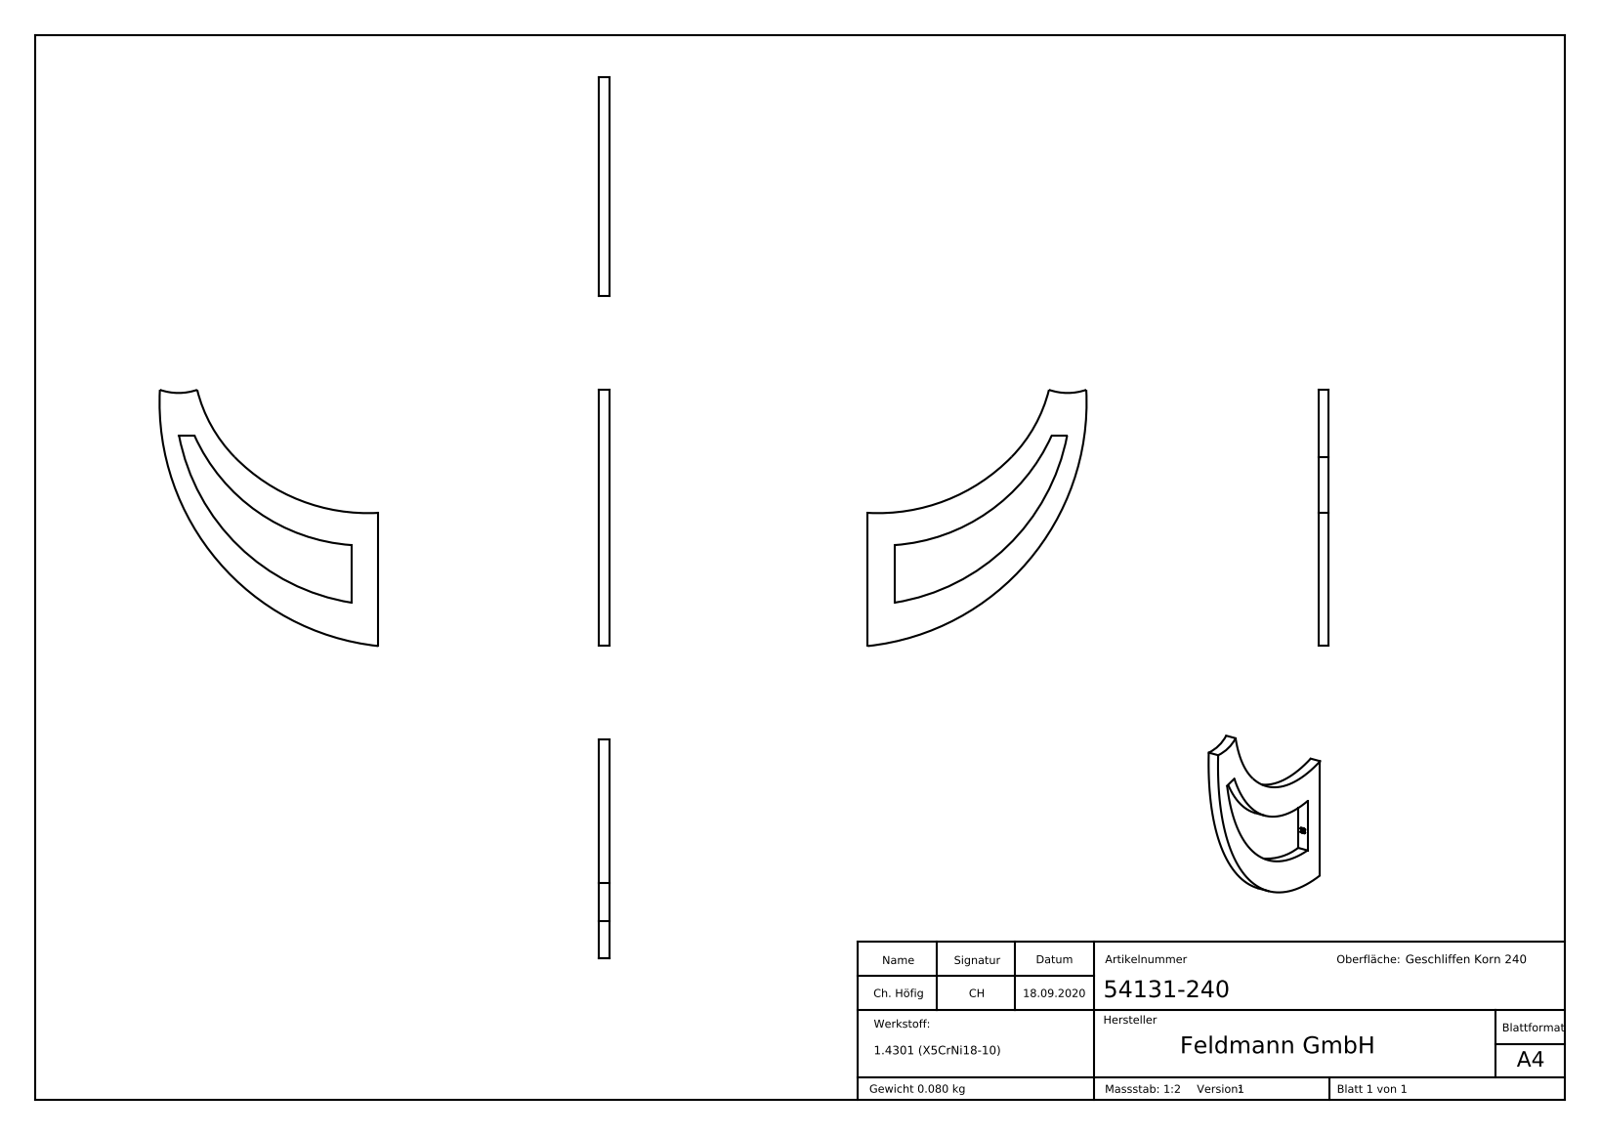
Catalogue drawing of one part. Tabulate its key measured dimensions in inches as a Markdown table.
| quantity | value |
| --- | --- |
| part name | 54131-240 |
| STEP written by | SolidWorks 2018 (CONFIG_CONTROL_DESIGN) |
| units | inches |
| bodies | 1 solid, 230 faces (139 planar, 6 cylindrical, 85 other) |
| overall size | 3.787 × 3.233 × 0.157 |
| volume | 0.617 in³ |
| surface area | 10.88 in² |
| partial cylindrical surfaces (radius × count) | 2.756 × 2, 0.835 × 1, 2.165 × 1, 3.091 × 1, 3.622 × 1 |
| main face-to-face distances | 0.157, 0.398, 0.394, 0.019, 0.045, 0.057, 0.062, 0.057, 0.059, 0.039 |
